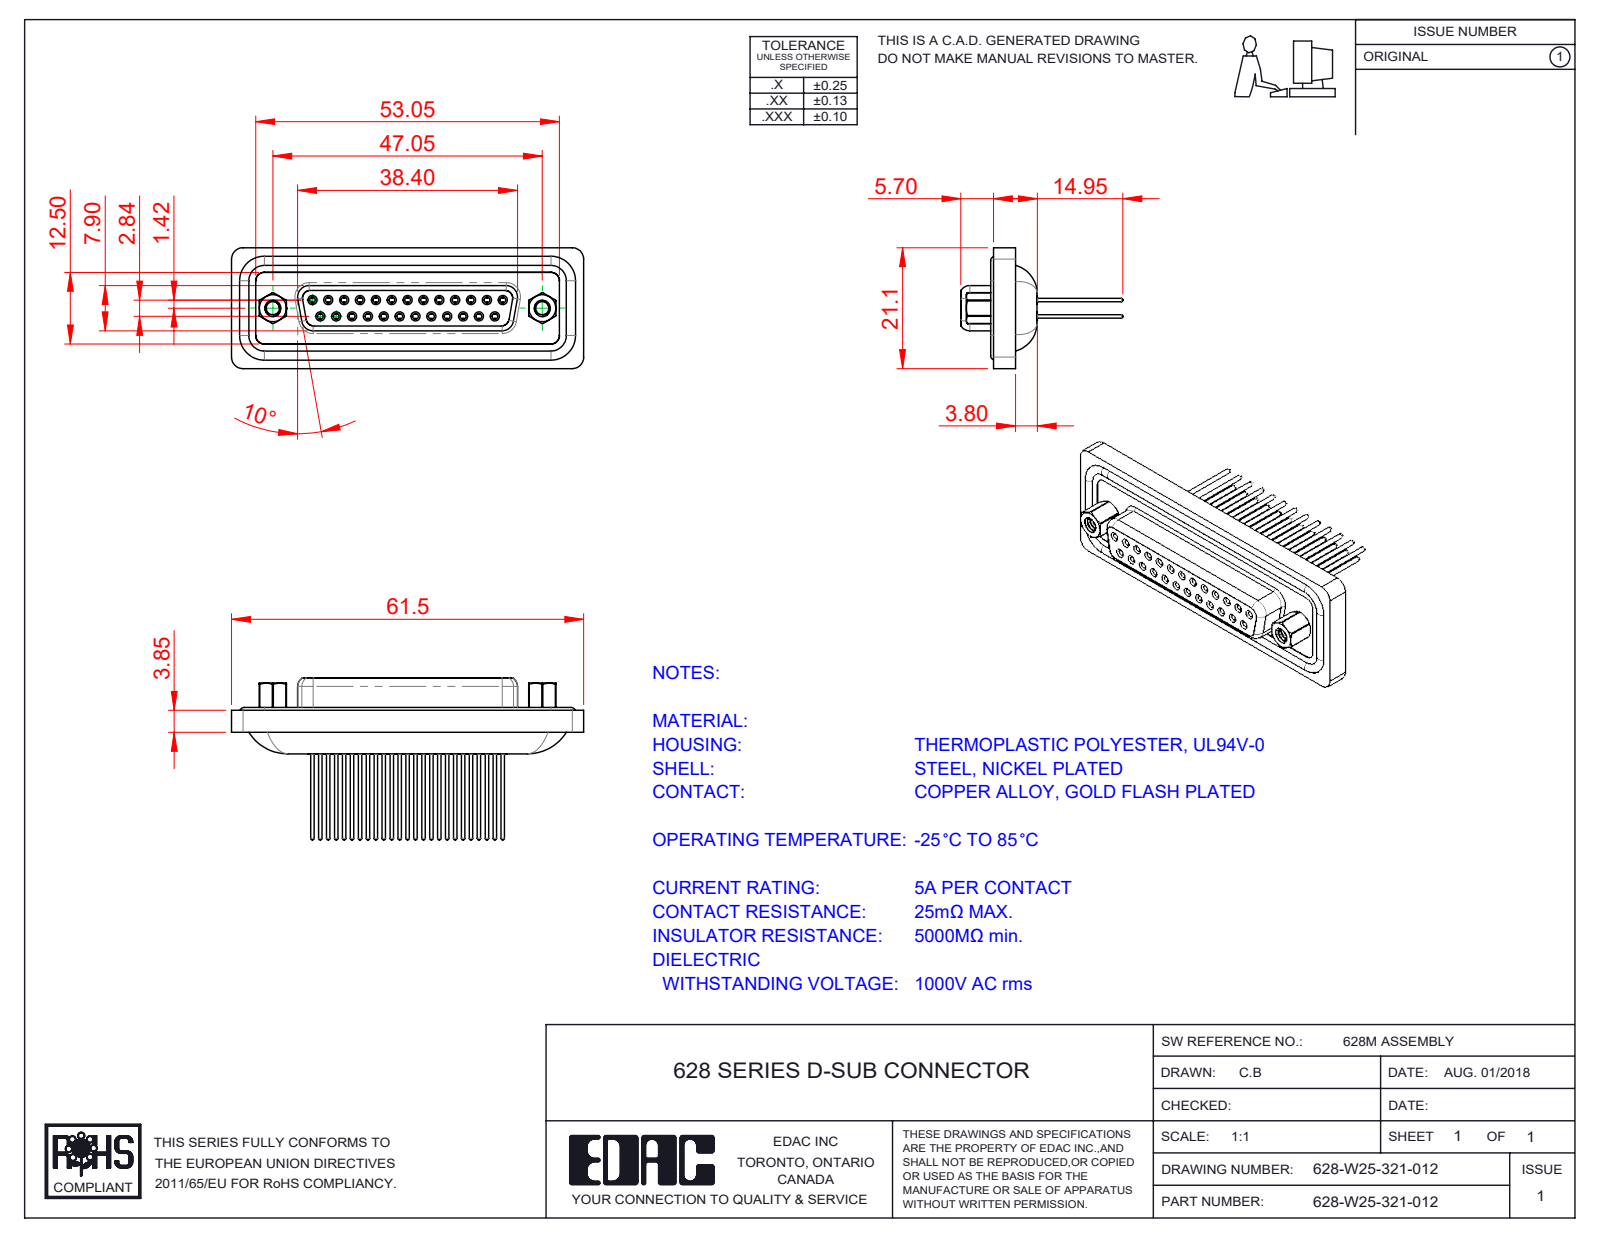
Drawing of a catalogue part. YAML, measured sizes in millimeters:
part_name: "628W Waterproof Housing_25 Contacts; 628W 4-40 Hex Standoff; 628W 4-40 Threaded Rivet; 628W Housing_25 Contacts (+4 more)"
step_written_by: "SolidWorks 2020 (CONFIG_CONTROL_DESIGN)"
units: millimeters
bodies: {solids: 33, faces: 1848, planar: 476, cylindrical: 745, other: 627}
overall_size: [61.5, 28.3, 21.1]
volume: 8569
surface_area: 13899
round_holes:
  - {diameter: 1, count: 25}
  - {diameter: 1.1, count: 25}
  - {diameter: 1.5, count: 25}
  - {diameter: 1.7, count: 25}
  - {diameter: 1.8, count: 25}
  - {diameter: 2, count: 25}
  - {diameter: 2.26, count: 2}
  - {diameter: 2.29, count: 2}
  - {diameter: 4, count: 2}
  - {diameter: 4.8, count: 2}
  - {diameter: 5, count: 2}
round_bosses_or_shafts:
  - {diameter: 1.6, count: 29}
  - {diameter: 2.2, count: 25}
  - {diameter: 0.6, count: 25}
  - {diameter: 4.9, count: 2}
  - {diameter: 2.79, count: 2}
partial_cylinders:
  - {radius: 2, count: 16}
  - {radius: 1.5, count: 14}
  - {radius: 1.35, count: 8}
  - {radius: 2.7, count: 6}
  - {radius: 0.5, count: 4}
  - {radius: 0.9, count: 4}
  - {radius: 1.6, count: 4}
  - {radius: 1.75, count: 4}
face_to_face_distances: [0.4, 7.45, 1.1, 2.75, 7.5, 3.75, 13.65, 0.5, 8.45, 6.2]
hole_center_spacings: [3.16, 2.77, 5.54, 8.31, 11.08, 13.85, 16.62, 5.03]
